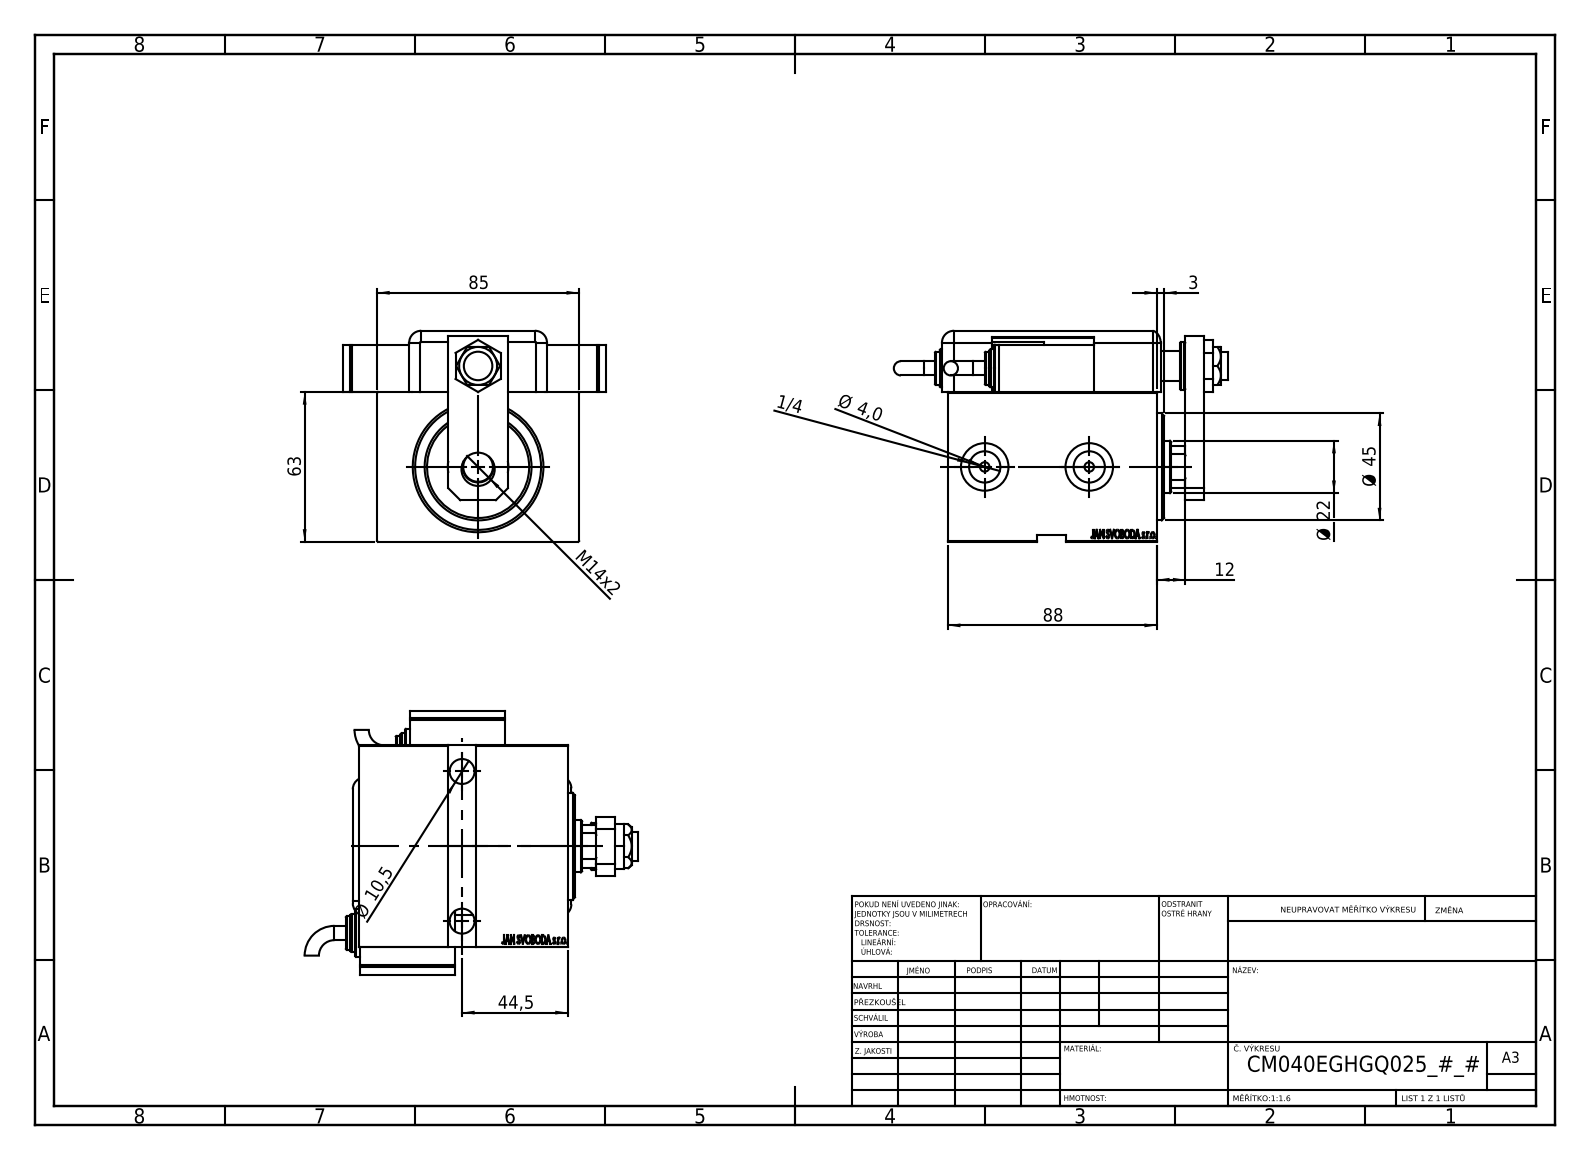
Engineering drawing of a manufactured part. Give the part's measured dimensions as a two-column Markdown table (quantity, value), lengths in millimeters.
| quantity | value |
| --- | --- |
| part name | SWITCH Q; SWITCH DIM A_G; V450CM_E_VCP; NUT_D19 (+7 more) |
| STEP written by | SolidWorks 2019 (CONFIG_CONTROL_DESIGN) |
| units | millimeters |
| bodies | 13 solids, 1230 faces (614 planar, 99 cylindrical, 517 other) |
| overall size | 140.46 × 111 × 88.8 |
| volume | 571 741 mm³ |
| surface area | 122 297 mm² |
| round holes (diameter × count) | 4 × 4, 8 × 2, 10.5 × 2, 13.16 × 2, 14 × 2, 16.5 × 2, 20 × 2, 12 × 1, 12.5 × 1, 13 × 1, 22 × 1, 25.5 × 1 |
| round bosses / shafts (diameter × count) | 20 × 3, 16 × 2, 14 × 2, 6 × 2, 45 × 1, 42 × 1 |
| partial cylindrical surfaces (radius × count) | 5 × 9, 10 × 1, 10.5 × 1 |
| main face-to-face distances | 3, 83, 63, 85, 88, 13.5, 12, 20, 1.5, 88.8 |
| hole center spacings | 41.5, 54.61, 1, 20, 42.5, 43.5, 44, 63 |
